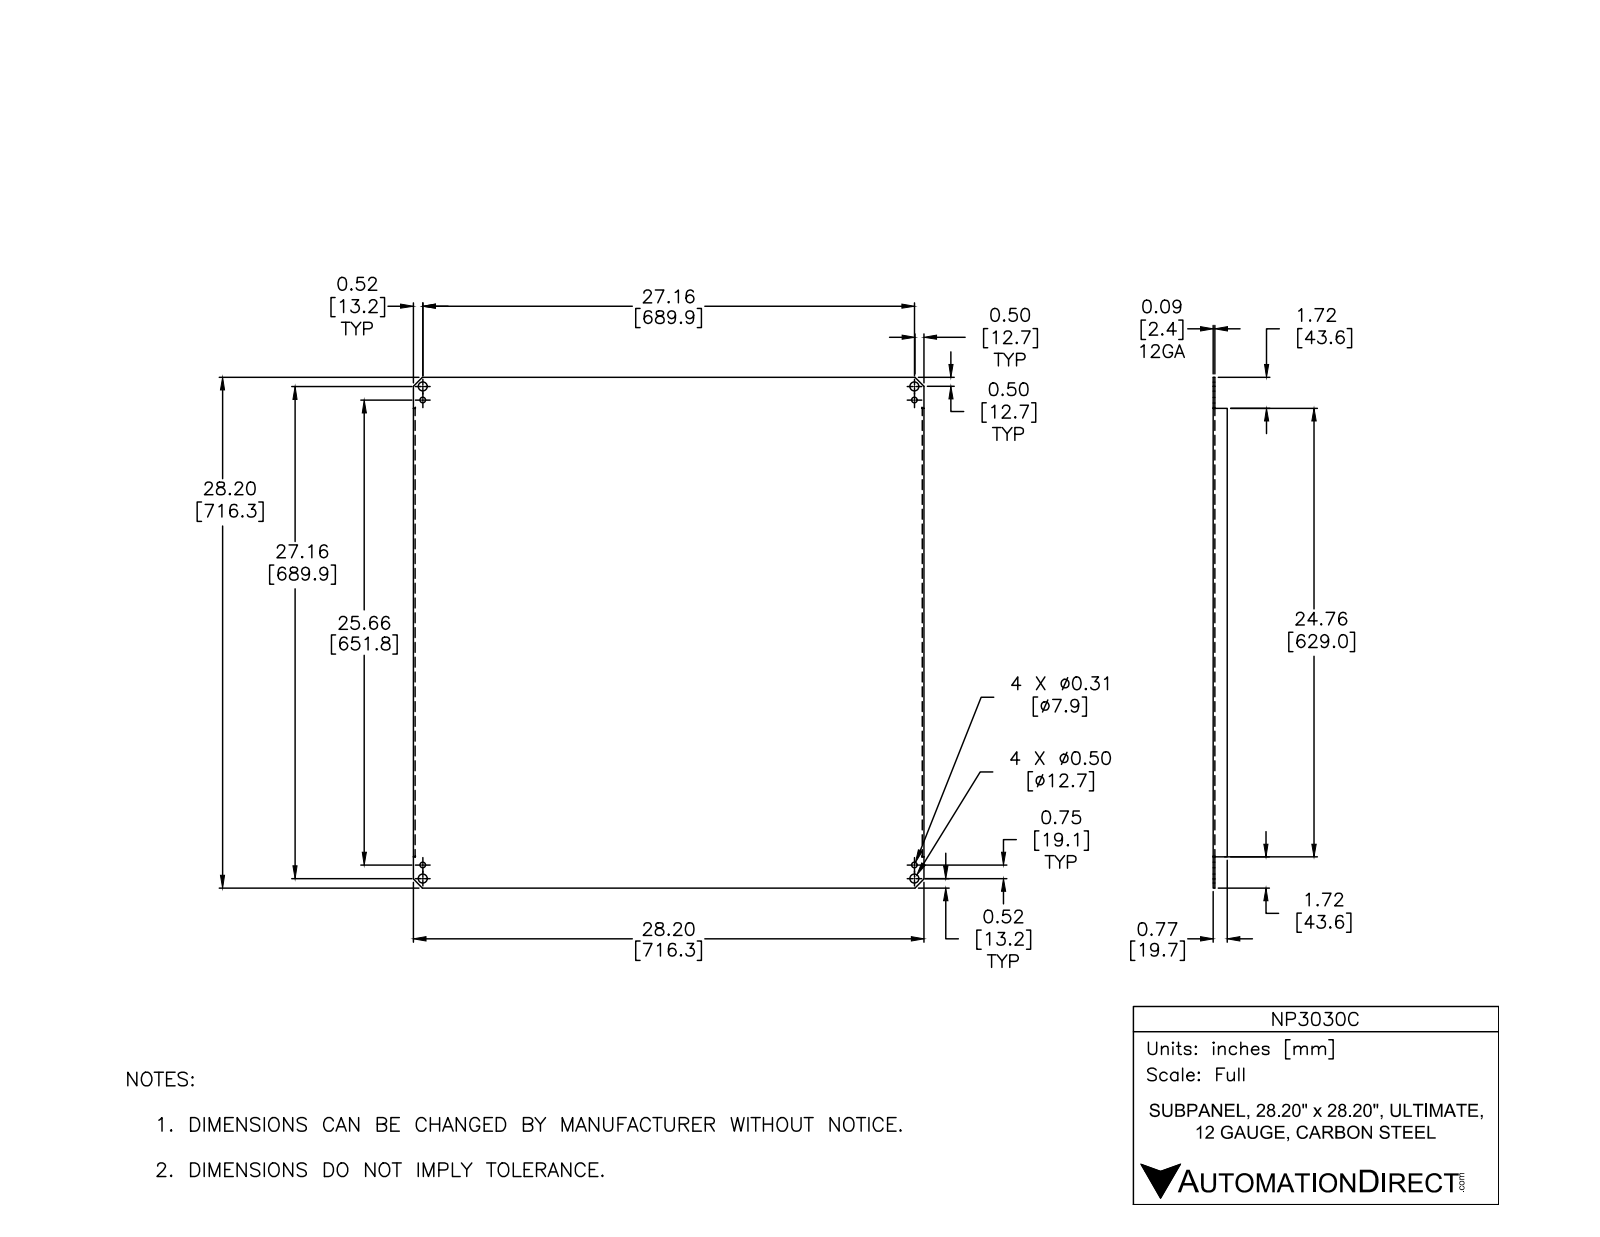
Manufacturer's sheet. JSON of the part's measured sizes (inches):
{"part_name": "NP3030C", "step_written_by": "Autodesk Inventor 2012 (AUTOMOTIVE_DESIGN)", "units": "inches", "bodies": {"solids": 1, "faces": 66, "planar": 50, "cylindrical": 16, "other": 0}, "overall_size": [28.2, 28.2, 0.774], "volume_in3": 80.47, "surface_area_in2": 1729, "round_holes": [[0.313, 4], [0.5, 4]], "partial_cylinders_radius": [[0.016, 4], [0.109, 4]], "face_to_face_distances": [0.094, 28.106, 28.2, 28.013, 0.68, 0.774, 1.718, 26.482, 1.624, 26.388], "hole_center_spacings": [27.16, 0.75, 26.41, 27.17, 37.883, 25.66, 37.364, 38.41]}
